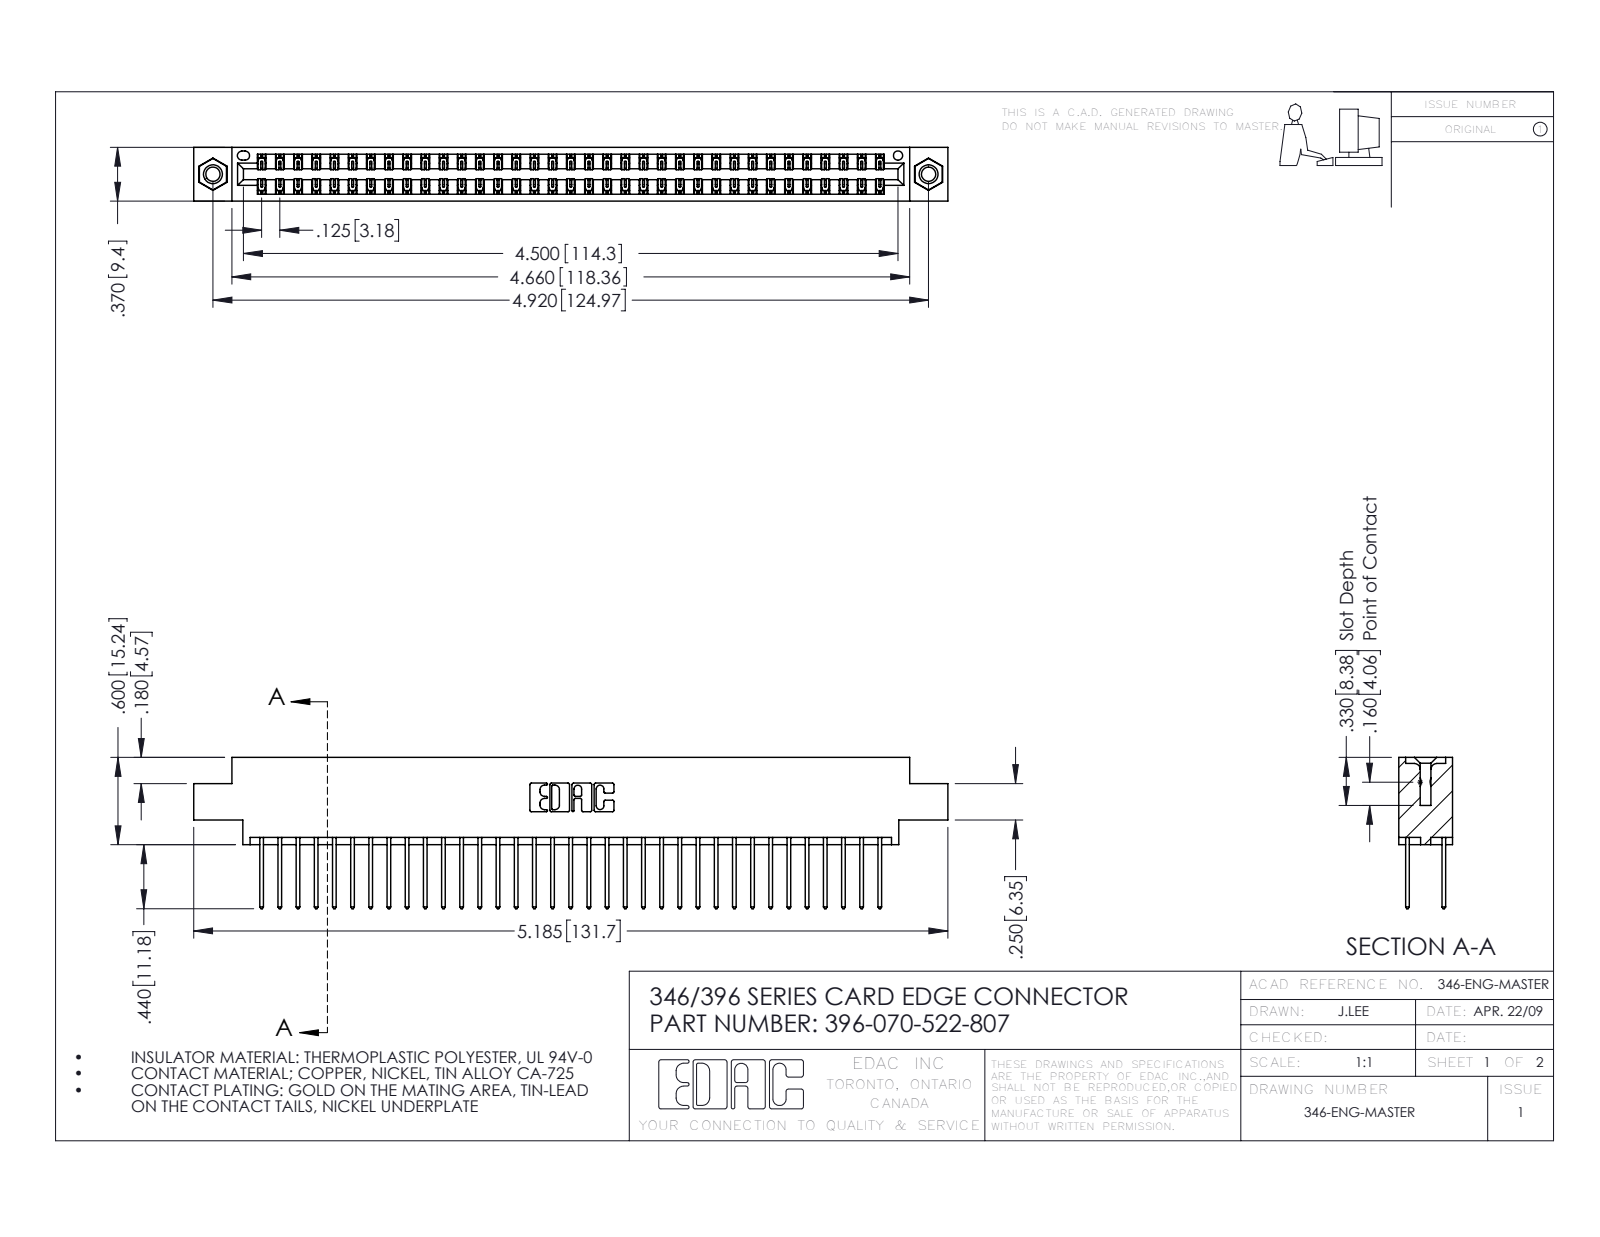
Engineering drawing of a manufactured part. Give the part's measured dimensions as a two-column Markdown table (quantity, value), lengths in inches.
| quantity | value |
| --- | --- |
| part name | 396-070-522-807; 345-292-001_345-293-122; 346 Part_0.170 Offset - 0.156 Dia-TI; 345-250-001_345-250-005-103 |
| STEP written by | SolidWorks 2016 (CONFIG_CONTROL_DESIGN) |
| units | inches |
| bodies | 73 solids, 3826 faces (2562 planar, 1248 cylindrical, 16 other) |
| overall size | 5.185 × 1.04 × 0.37 |
| volume | 0.781 in³ |
| surface area | 28.72 in² |
| round holes (diameter × count) | 0.098 × 2, 0.125 × 2, 0.156 × 2, 0.064 × 1 |
| round bosses / shafts (diameter × count) | 0.155 × 2 |
| partial cylindrical surfaces (radius × count) | 0.006 × 105, 0.01 × 70, 0.01 × 22, 0.007 × 6, 0.031 × 6, 0.026 × 3, 0.014 × 2, 0.022 × 2 |
| main face-to-face distances | 0.048, 0.322, 0.25, 0.37, 0.072, 0.298, 0.025, 0.275, 0.222, 0.148 |
| hole center spacings | 0.246, 4.711, 4.92 |
